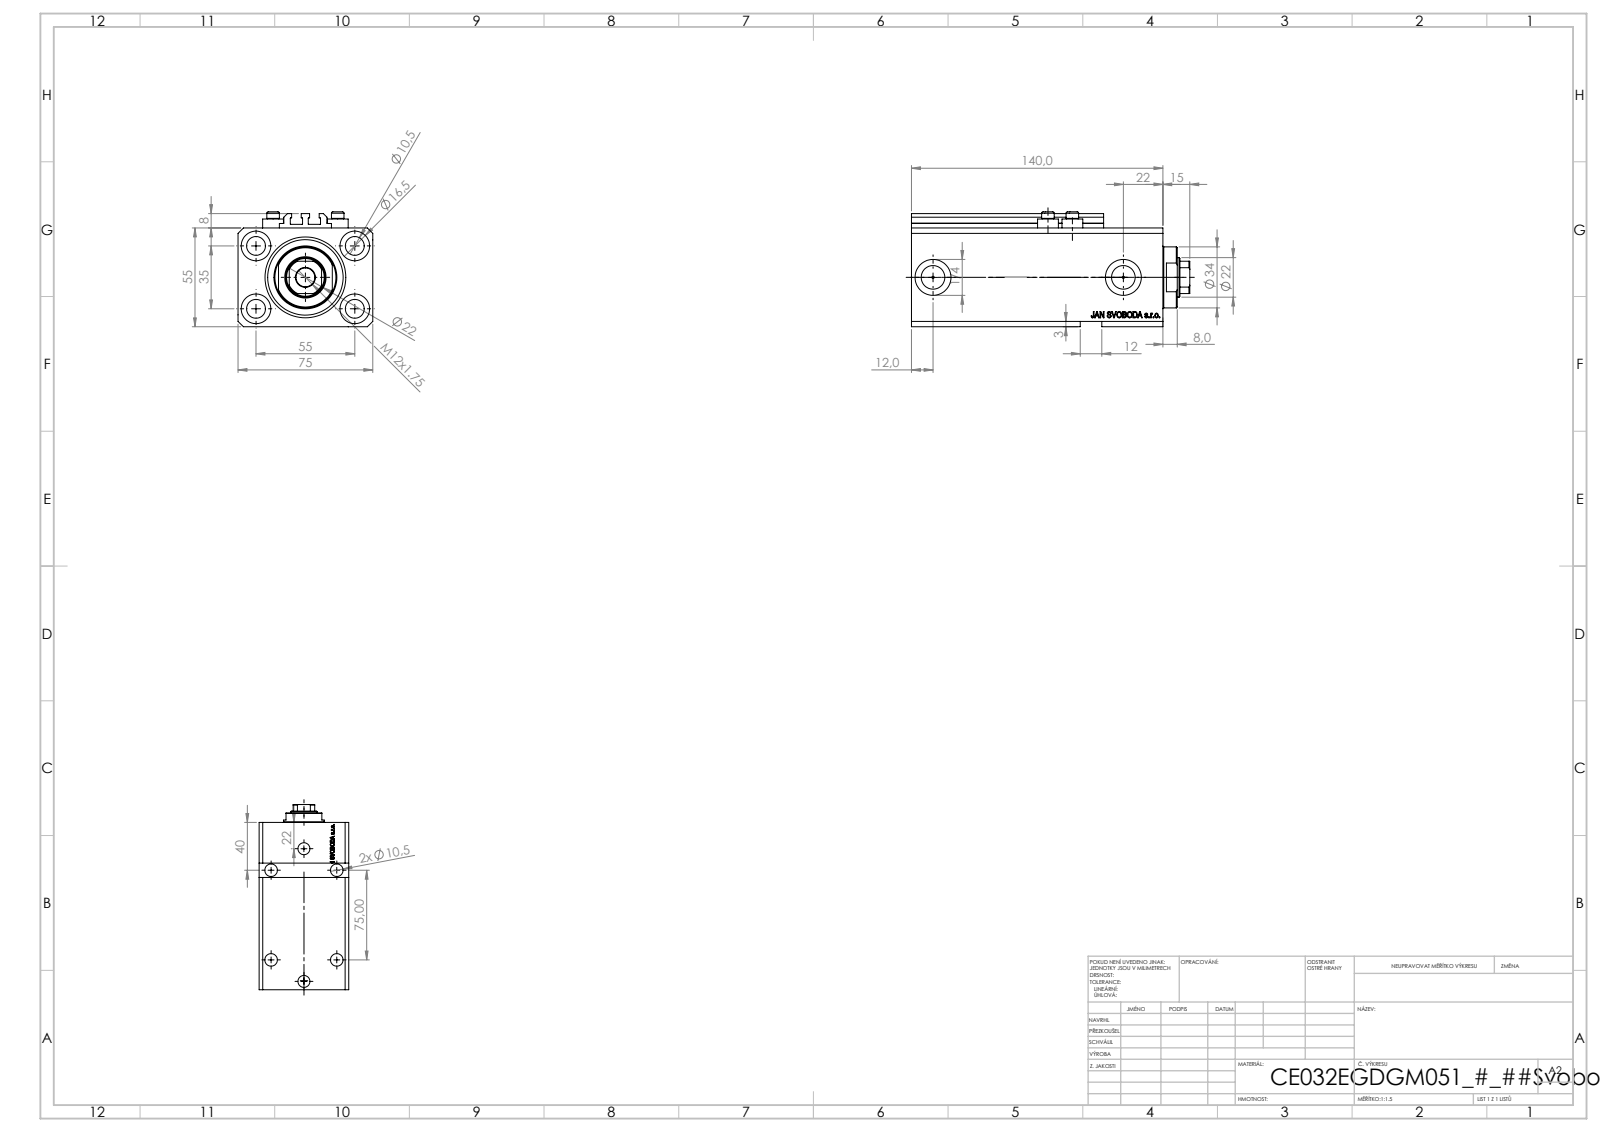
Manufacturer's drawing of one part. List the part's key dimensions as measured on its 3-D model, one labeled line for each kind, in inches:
Part name (STEP PRODUCT): V250CE_C_VCP; V250CE_E_Body; V250CE_VC_E; ALLEN BOLT V250CE
STEP written by: SolidWorks 2019 (CONFIG_CONTROL_DESIGN)
Units: inches
Bodies: 8 solids, 1100 faces (518 planar, 158 cylindrical, 424 other)
Overall size (bounding box): 6.102 × 2.953 × 2.52
Volume: 29.39 in³ · Surface area: 180.5 in²
Round holes (diameter × count): ⌀0.413 ×9, ⌀0.049 ×4, ⌀0.157 ×4, ⌀0.65 ×4, ⌀0.394 ×2, ⌀0.518 ×2, ⌀0.787 ×2, ⌀0.866 ×1, ⌀1.26 ×1, ⌀1.772 ×1
Round bosses / shafts (diameter × count): ⌀0.457 ×4, ⌀0.276 ×4, ⌀1.339 ×1
Partial cylindrical surfaces — rounded edges, fillets, slot ends (radius × count): R0.008 ×10, R0.413 ×1
Main face-to-face distances: 2.165, 2.953, 0.591, 0.39, 5.512, 4.921, 0.118, 2.244, 4.531, 5.122
Hole centre spacings: 1.283, 1.294, 2.165, 3.818, 0.535, 0.555, 1.016, 1.283
